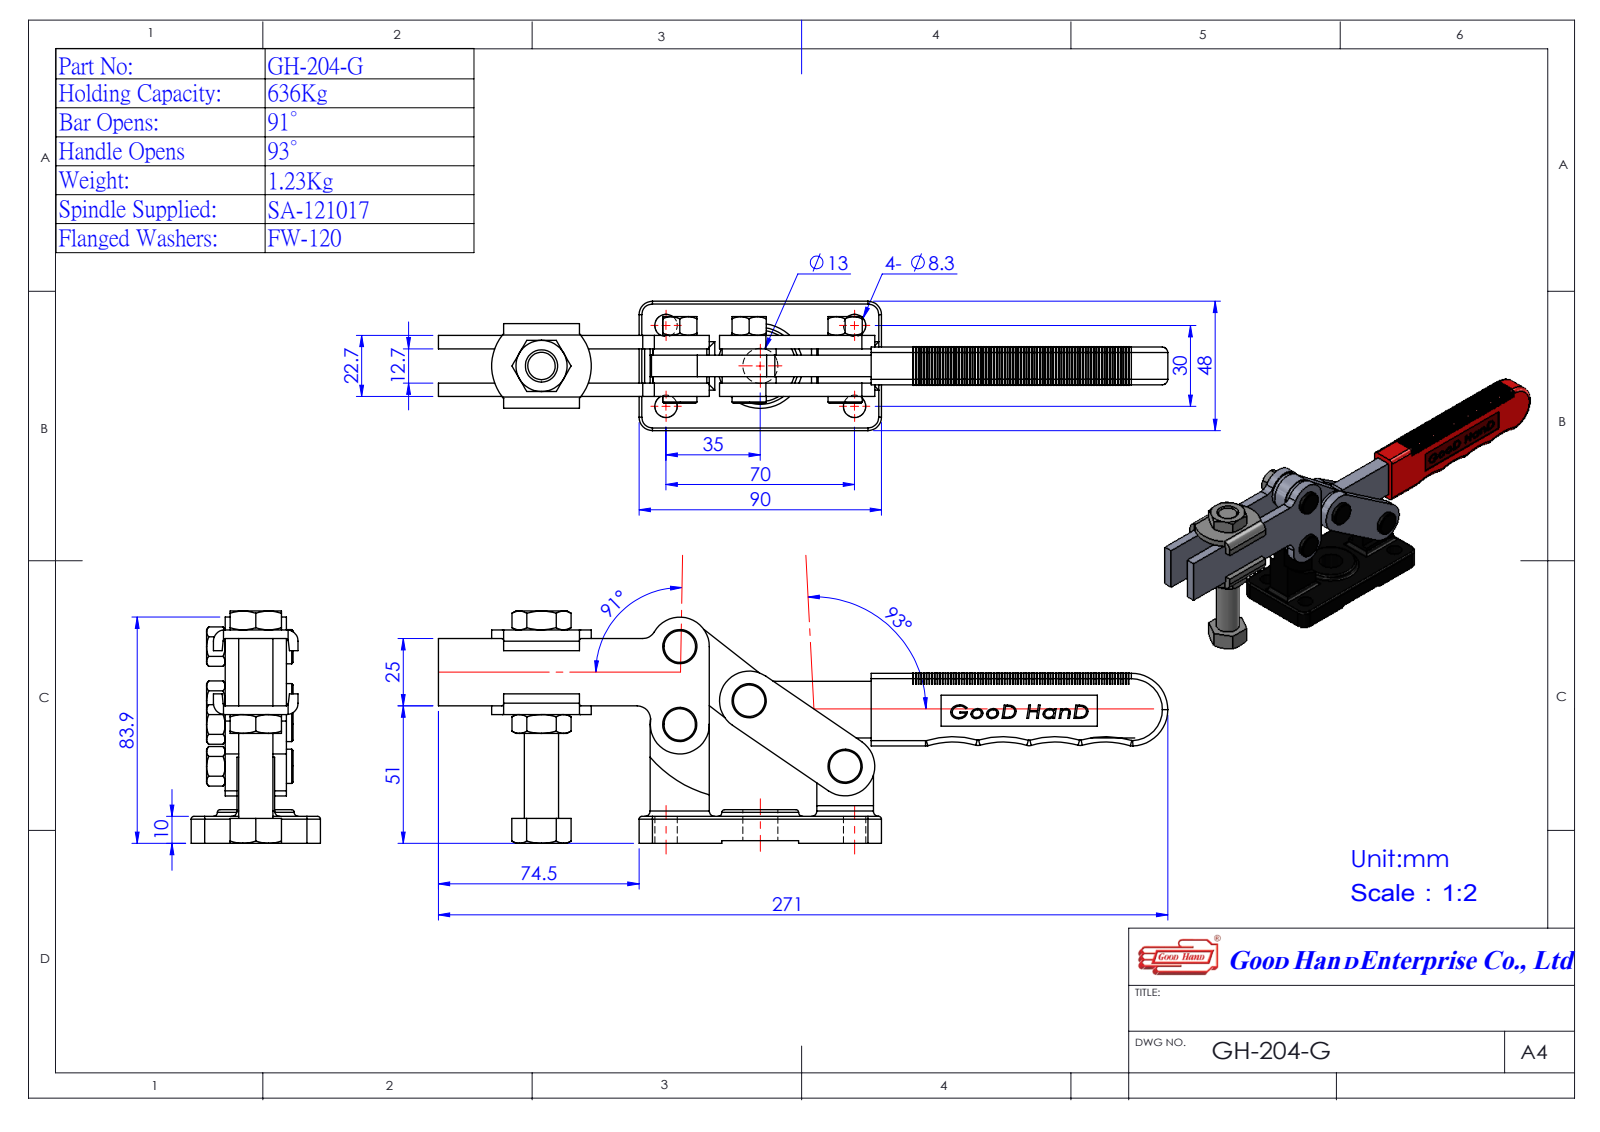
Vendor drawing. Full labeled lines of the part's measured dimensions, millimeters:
Part name (STEP PRODUCT): Group2^GH-204-G(簡化)-1; Group3^GH-204-G(簡化)-1; Group5^GH-204-G(簡化)-1; 2204G13-1^GH-204-G(簡化)-1 (+2 more)
STEP written by: SolidWorks 2016 (AUTOMOTIVE_DESIGN)
Units: millimetres
Bodies: 4 solids, 361 faces (145 planar, 120 cylindrical, 96 other)
Overall size (bounding box): 270.8 × 109.25 × 48
Volume: 162 228 mm³ · Surface area: 69 954 mm²
Round holes (diameter × count): ⌀8 ×4, ⌀8.3 ×4, ⌀13 ×1
Round bosses / shafts (diameter × count): ⌀12.7 ×5, ⌀20 ×4, ⌀28.5 ×1
Partial cylindrical surfaces — rounded edges, fillets, slot ends (radius × count): R5 ×8, R2 ×6, R3 ×5, R1 ×4, R4.2 ×4, R32 ×4, R11 ×3, R10.5 ×2
Main face-to-face distances: 7.35, 15.35, 3, 4.35, 18.35, 11, 5, 17.7, 0.65, 13.35
Hole centre spacings: 38.08, 30, 70, 76.16, 27.24, 28.9, 32.63, 43.14
